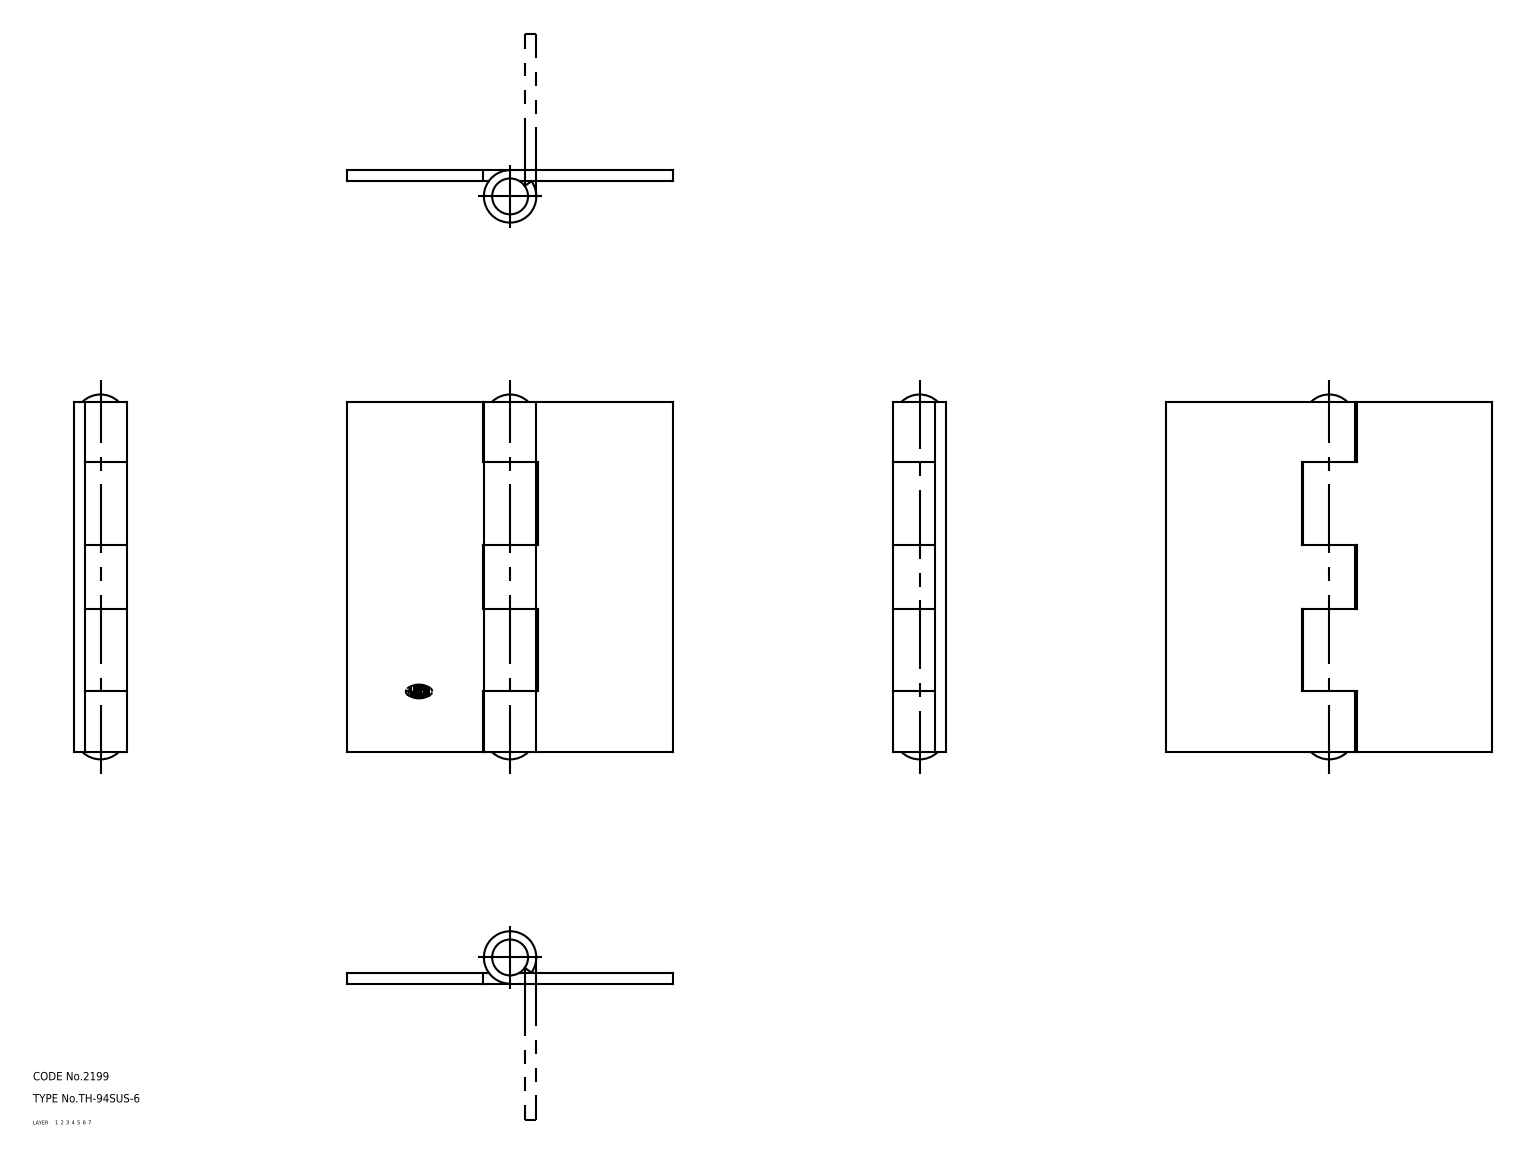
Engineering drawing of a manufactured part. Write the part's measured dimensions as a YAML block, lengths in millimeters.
part_name: "hinge piece_B; hinge piece_A; shaft; TH_94SUS_6_19495_36"
step_written_by: "CADfix (AUTOMOTIVE_DESIGN)"
units: millimeters
bodies: {solids: 3, faces: 44, planar: 0, cylindrical: 0, other: 44}
overall_size: [132.2, 118, 19]
volume: 87602
surface_area: 47163
